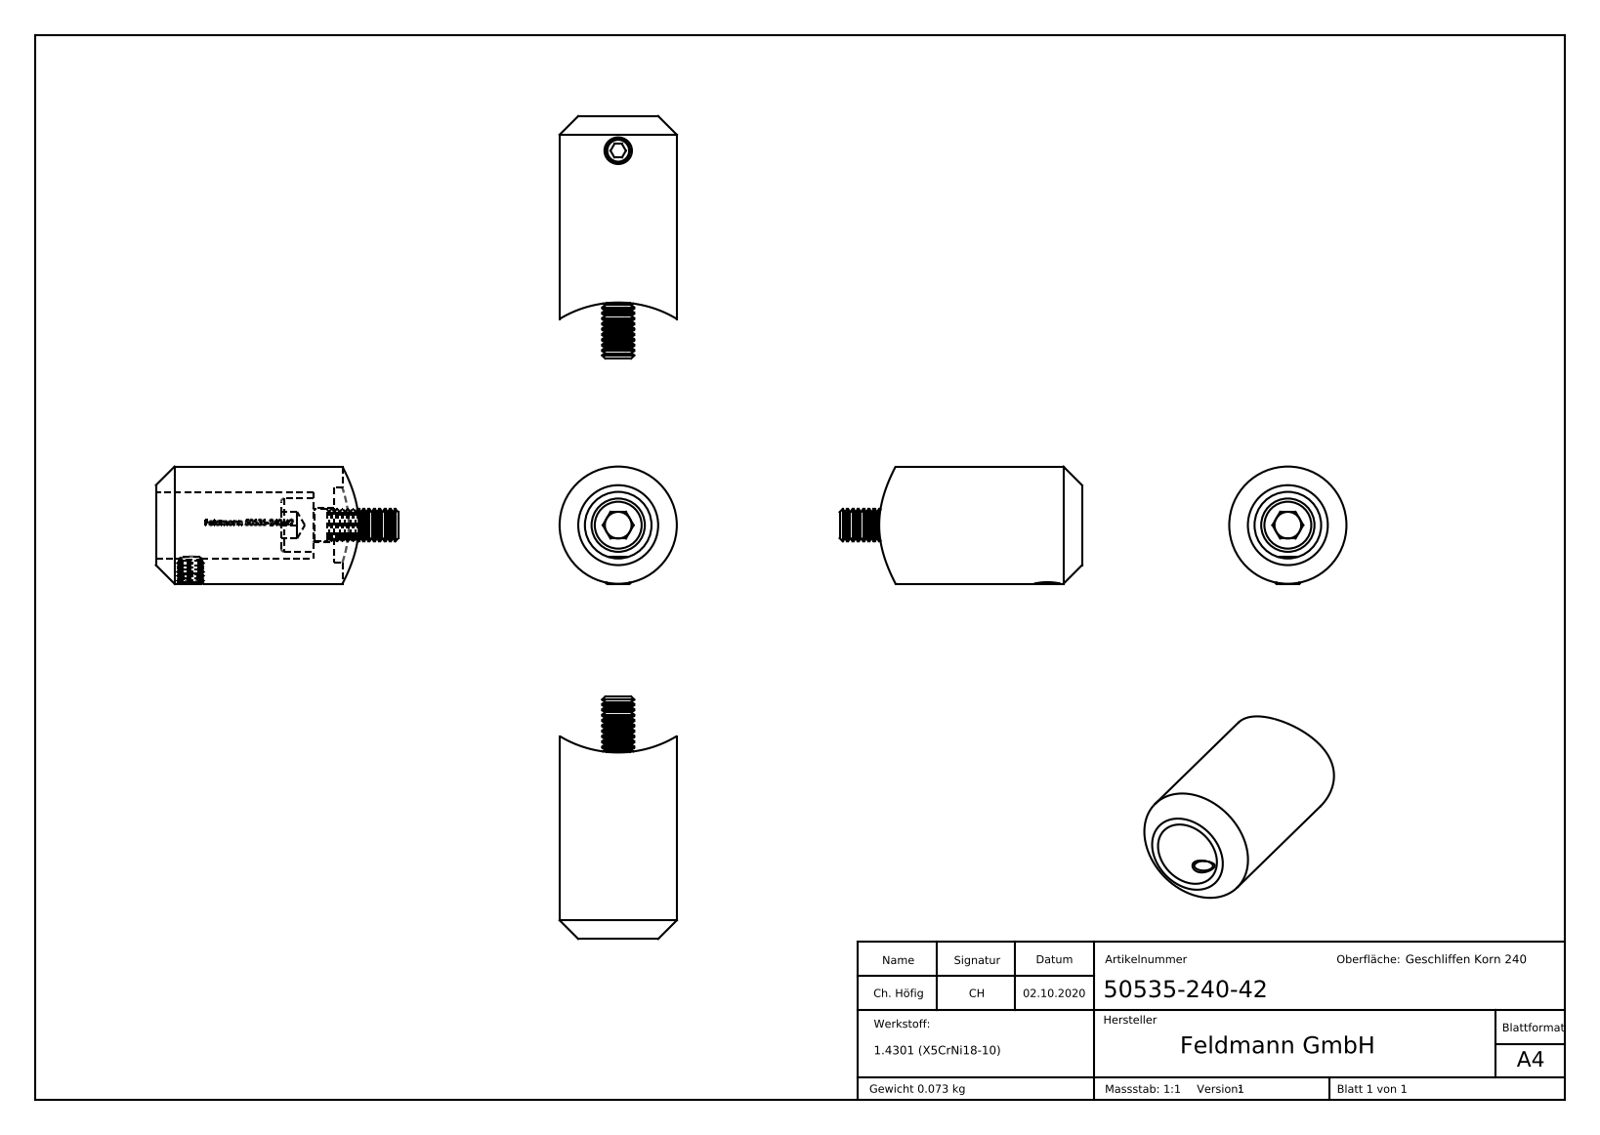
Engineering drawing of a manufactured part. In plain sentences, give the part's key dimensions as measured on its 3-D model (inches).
The part is named "socket head cap screw_din_DIN 912 M6 x 16 --- 16S; 50535-240-XX Teil1_50535-240-42 Teil1; 50535-240-42; 50535-240-XX Teil1 (+3 more)". Its 3-D file was written by "SolidWorks 2018 (CONFIG_CONTROL_DESIGN)". It is 3 solids with 441 faces: 168 planar, 65 cylindrical and 208 other. Overall it measures 1.791 by 0.866 by 0.866 inches. Its volume is 0.609 cubic inches and its surface area 8.365 square inches. Round holes: 1 of diameter 0.165, 1 of diameter 0.256, 1 of diameter 0.492, 1 of diameter 0.551. Round bosses or shafts: 1 of diameter 0.866, 1 of diameter 0.394, 1 of diameter 0.236, 1 of diameter 0.197. Partial cylindrical surfaces (rounded edges, fillets, slot ends): 1 of radius 0.835. The main face-to-face distances are 0.157, 1.319, 1.161, 0.236, 0.394, 0.925, 0.198, 0.472, 0.63, 0.866.
